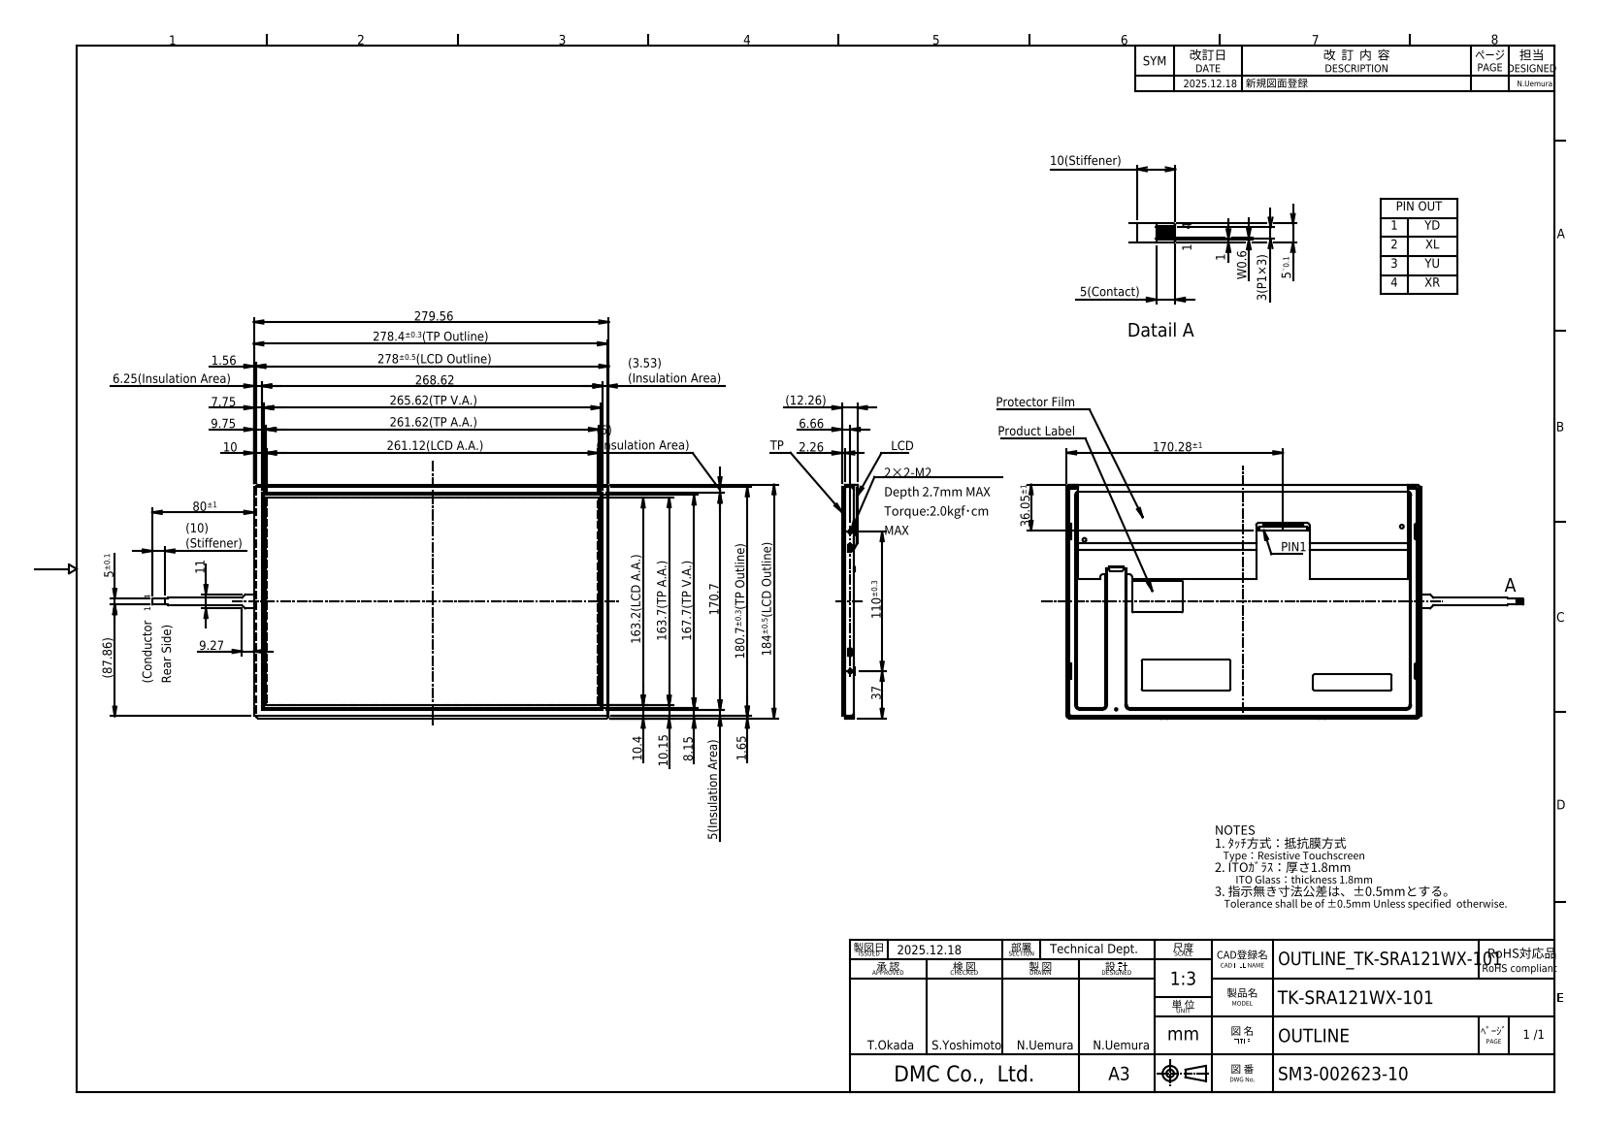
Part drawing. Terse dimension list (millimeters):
name: HP-TK-SRA121WX-101
written by: Autodesk Inventor 2024 (AUTOMOTIVE_DESIGN)
unit: mm
bodies: 1 solid, 4390 faces (2981 planar, 1086 cylindrical, 323 other)
size: 359.56 × 184.05 × 12.25
volume: 210 998 mm³; area: 306 748 mm²
holes: 4× ⌀1, 4× ⌀2, 3× ⌀1.8, 2× ⌀3, 2× ⌀3.2, 2× ⌀5.03
bosses: 4× ⌀4, 2× ⌀3, 1× ⌀2.1
rounds: 193× R0.5, 154× R1, 143× R0.2, 133× R0.3, 95× R0.1, 39× R0.4, 36× R0.9, 33× R0.8
face distances: 0.8, 2.99, 7.87, 4.88, 8.67, 5.68, 3.43, 0.9, 12.1, 9.11
hole spacings: 180.1, 274.1, 327.97, 4, 10.95, 11.45, 12.13, 23.39
